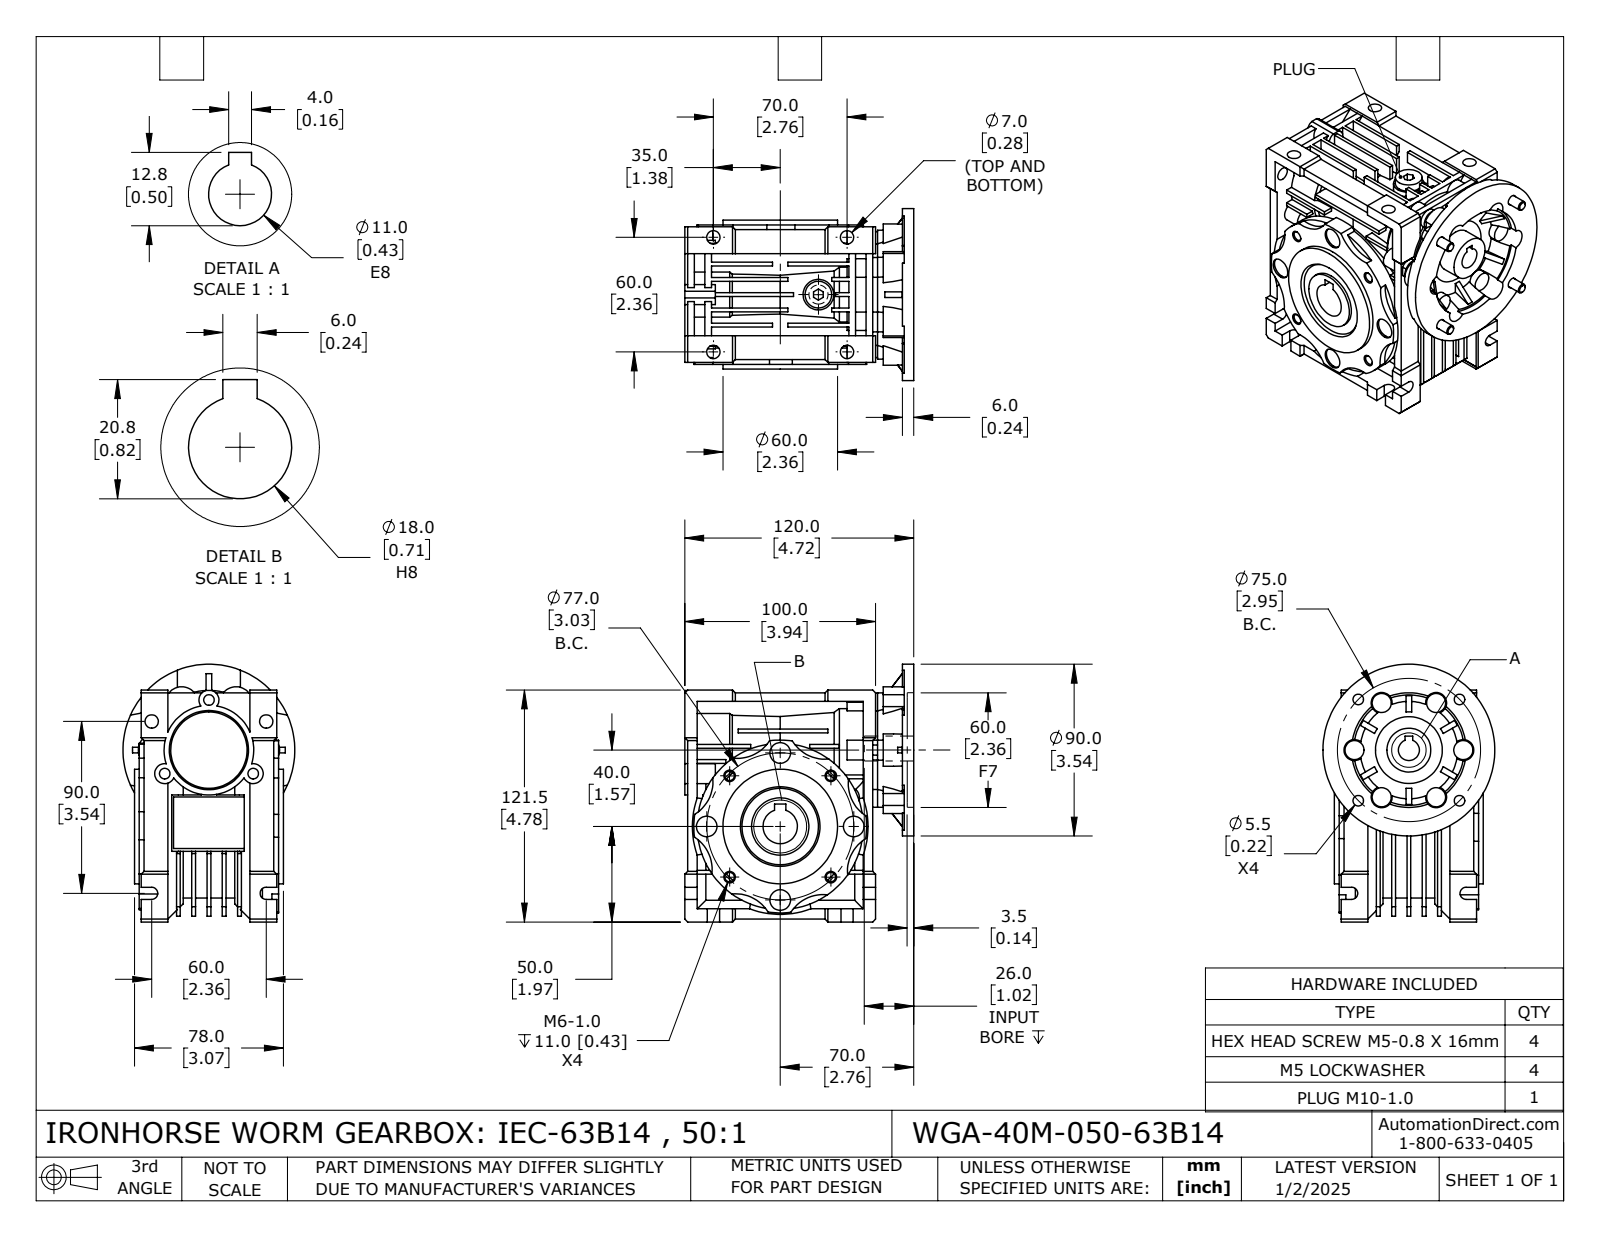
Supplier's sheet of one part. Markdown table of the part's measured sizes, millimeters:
| quantity | value |
| --- | --- |
| part name | WGA-40M-050-63B14 |
| STEP written by | SolidWorks 2024 (CONFIG_CONTROL_DESIGN) |
| units | millimeters |
| bodies | 14 solids, 1003 faces (564 planar, 307 cylindrical, 132 other) |
| overall size | 135 × 127.7 × 90 |
| volume | 667 307 mm³ |
| surface area | 163 100 mm² |
| round holes (diameter × count) | 7 × 6, 4.92 × 4, 5.1 × 4, 5.5 × 4, 10.8 × 4, 5.55 × 3, 9 × 1, 11 × 1, 11.5 × 1, 18 × 1, 23 × 1, 28 × 1 |
| round bosses / shafts (diameter × count) | 10 × 6, 9.2 × 4, 5 × 4, 90 × 1, 75 × 1, 60 × 1, 54 × 1, 47 × 1 |
| partial cylindrical surfaces (radius × count) | 5.25 × 9, 20 × 8, 3.2 × 6, 5.22 × 6, 5.5 × 6, 8.5 × 6, 5.51 × 4, 30 × 1 |
| main face-to-face distances | 8, 6, 2, 1.5, 16, 10, 5, 14, 2.5, 19 |
| hole center spacings | 29.1, 37.5, 53.04, 70.22, 33.54, 38.5, 54.45, 75.01 |
